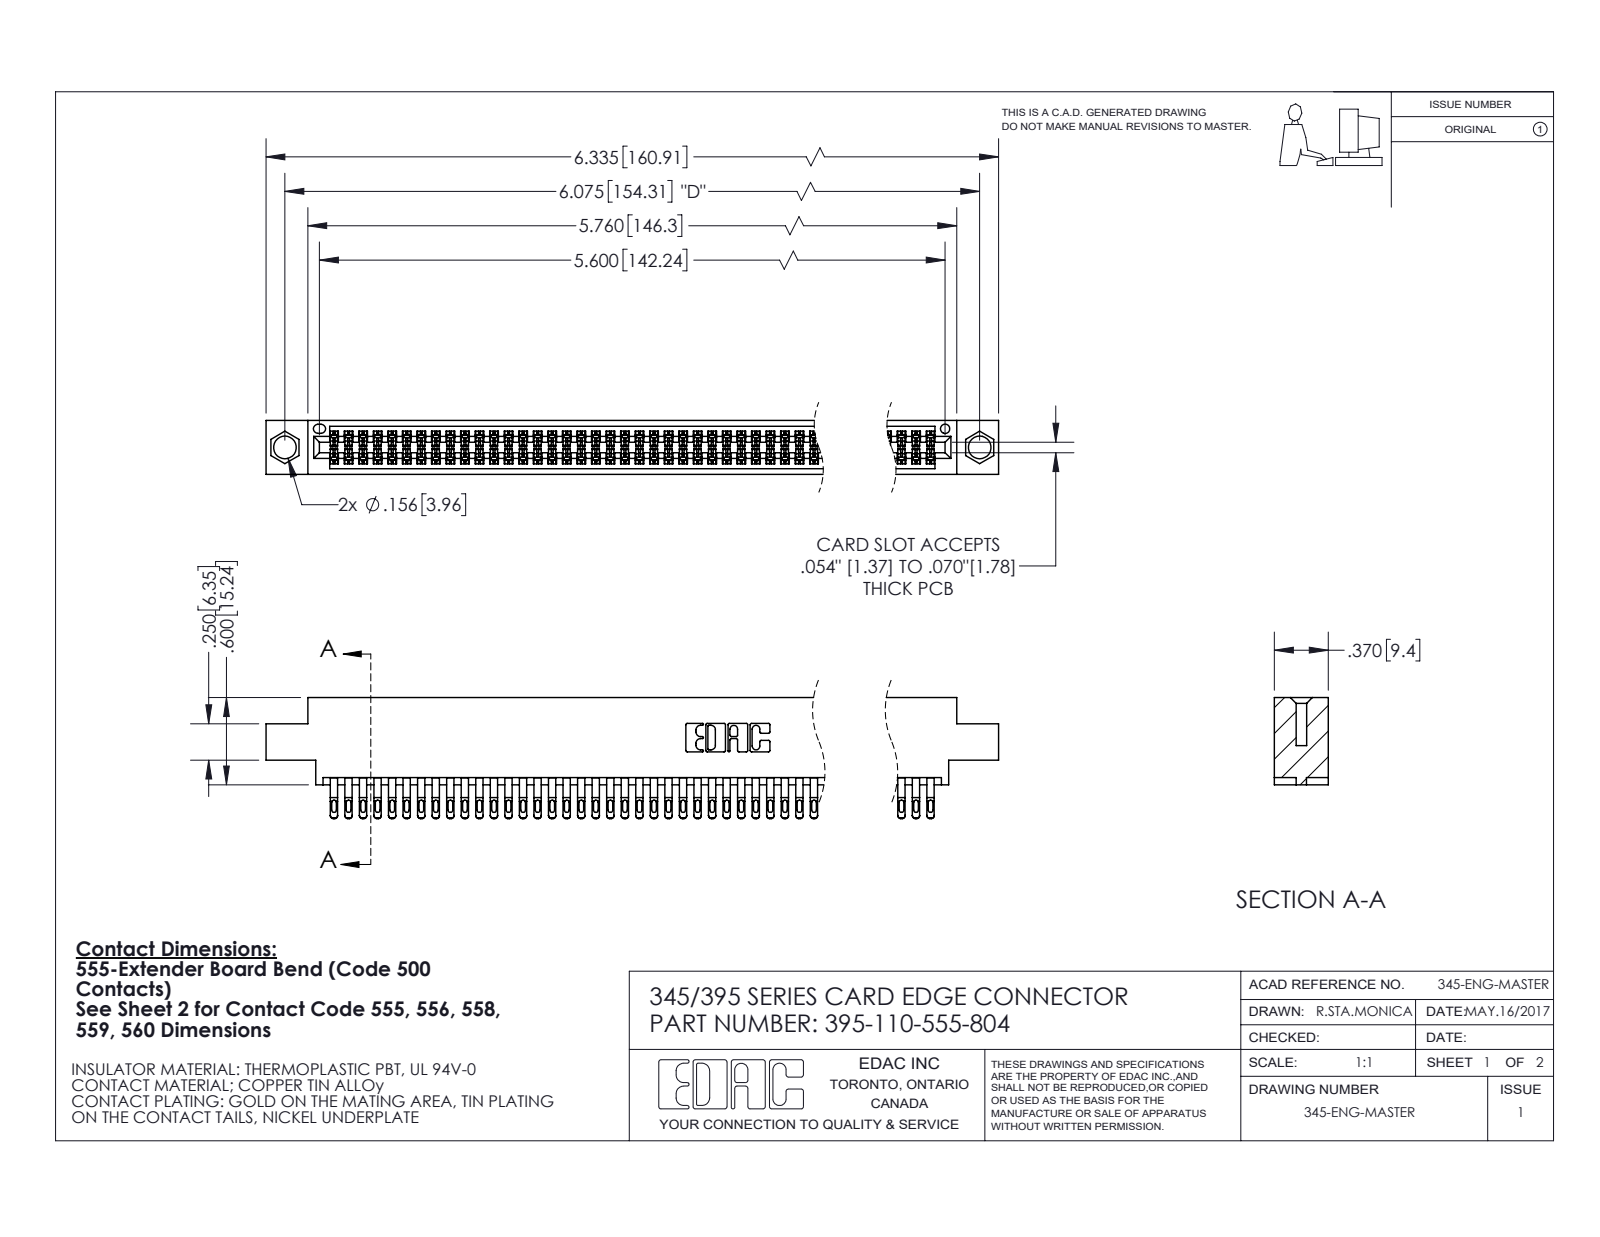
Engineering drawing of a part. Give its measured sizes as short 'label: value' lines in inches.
name: 345-292-001_555 Tail; 395-110-555-804; 345 Part_0.170 Offset - 0.156 Dia-TI
written by: SolidWorks 2020 (CONFIG_CONTROL_DESIGN)
unit: in
bodies: 111 solids, 6304 faces (3508 planar, 2796 cylindrical, 0 other)
size: 6.335 × 0.832 × 0.37
volume: 0.967 in³; area: 38.42 in²
holes: 2× ⌀0.156, 1× ⌀0.064
rounds: 275× R0.016, 220× R0.006, 220× R0.02, 22× R0.01, 6× R0.007, 6× R0.031, 3× R0.026, 2× R0.01
face distances: 0.072, 0.298, 0.37, 0.025, 0.2, 0.098, 0.272, 0.225, 0.175, 0.149
hole spacings: 0.27, 5.839, 6.075
